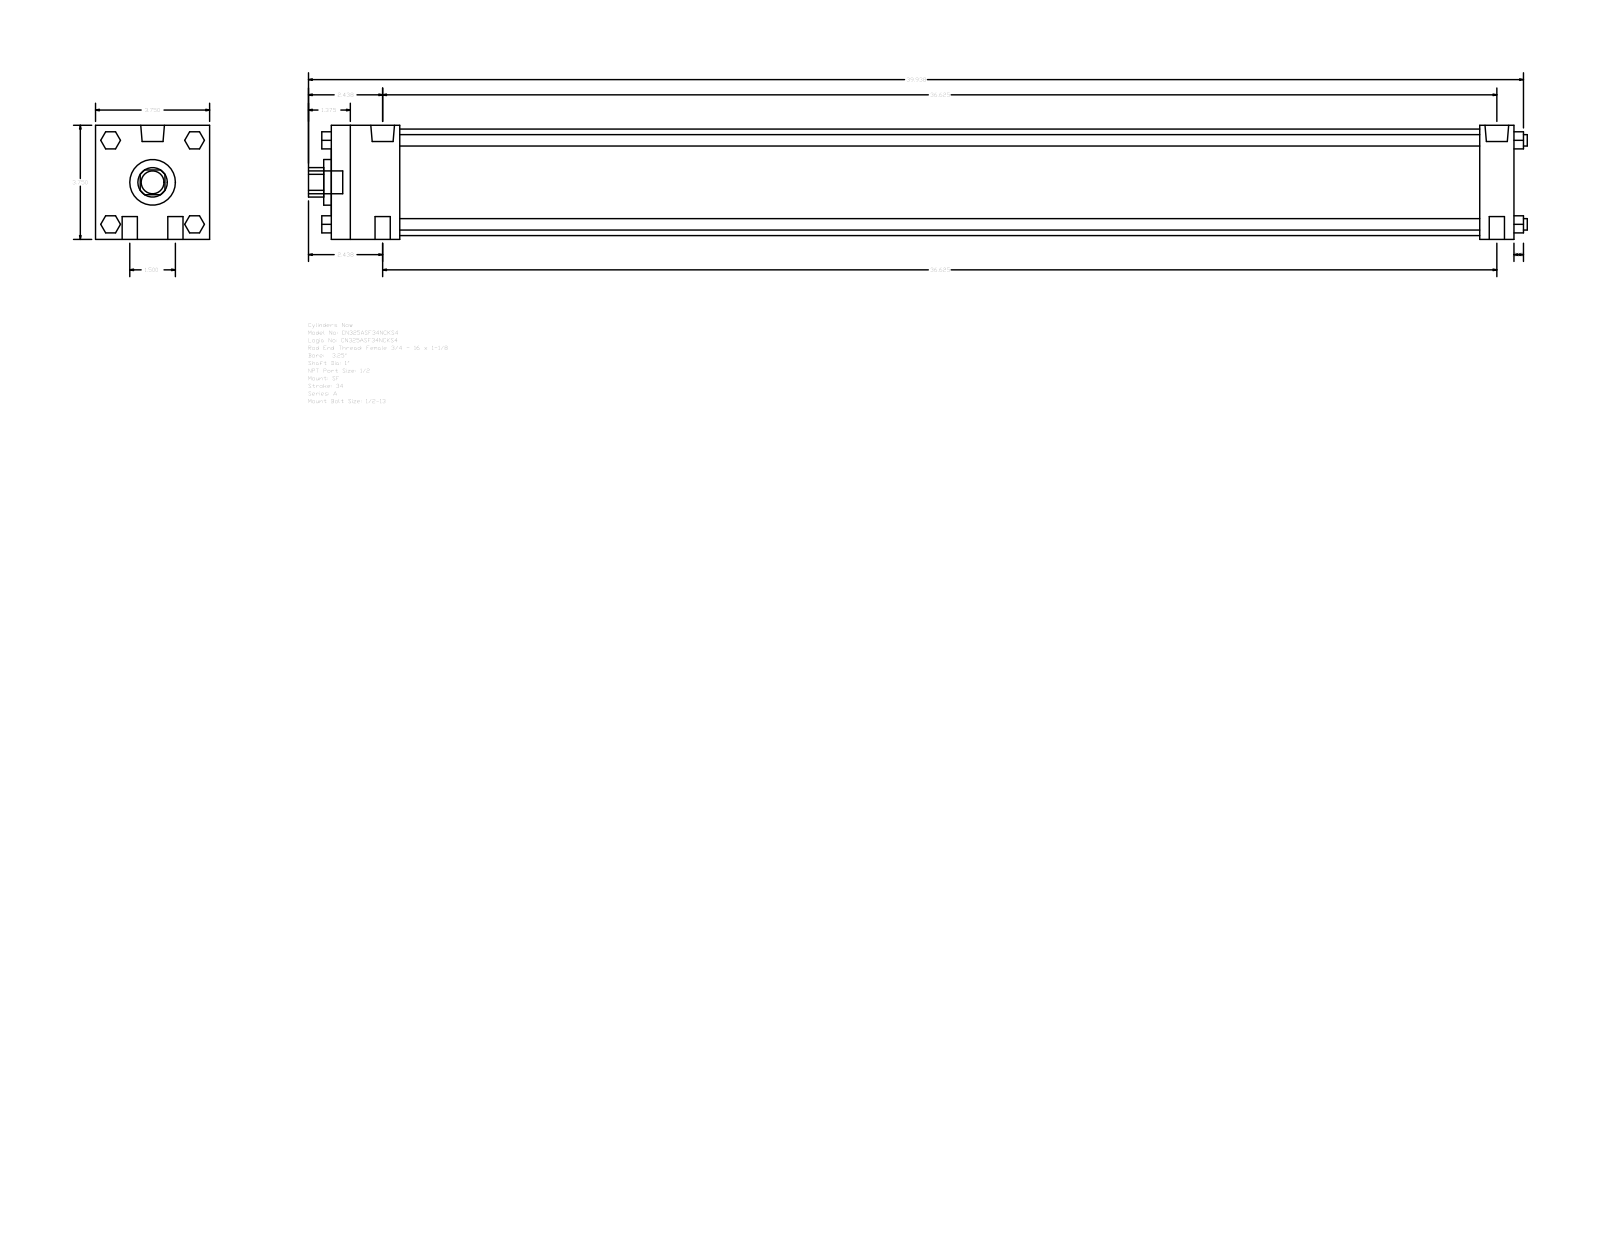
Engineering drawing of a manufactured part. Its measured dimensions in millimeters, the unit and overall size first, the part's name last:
Units: millimetres
Overall size (bounding box): 1017.59 × 95.25 × 95.25
Round holes (diameter × count): ⌀25.4 ×1, ⌀38.1 ×1, ⌀88.9 ×1
Round bosses / shafts (diameter × count): ⌀12.7 ×4, ⌀9.53 ×4, ⌀19.77 ×2, ⌀8.73 ×2, ⌀19.05 ×1
Partial cylindrical surfaces — rounded edges, fillets, slot ends (radius × count): R12.29 ×1
Main face-to-face distances: 95.24, 987.43, 958.85, 28.58, 57.15, 901.7, 930.28, 14.28, 35.05, 60.71
Bodies: 0 solids, 124 faces (94 planar, 30 cylindrical, 0 other)
Part name (STEP PRODUCT): A_SF__0325_1
STEP written by: GSSL Pune (CONFIG_CONTROL_DESIGN)
